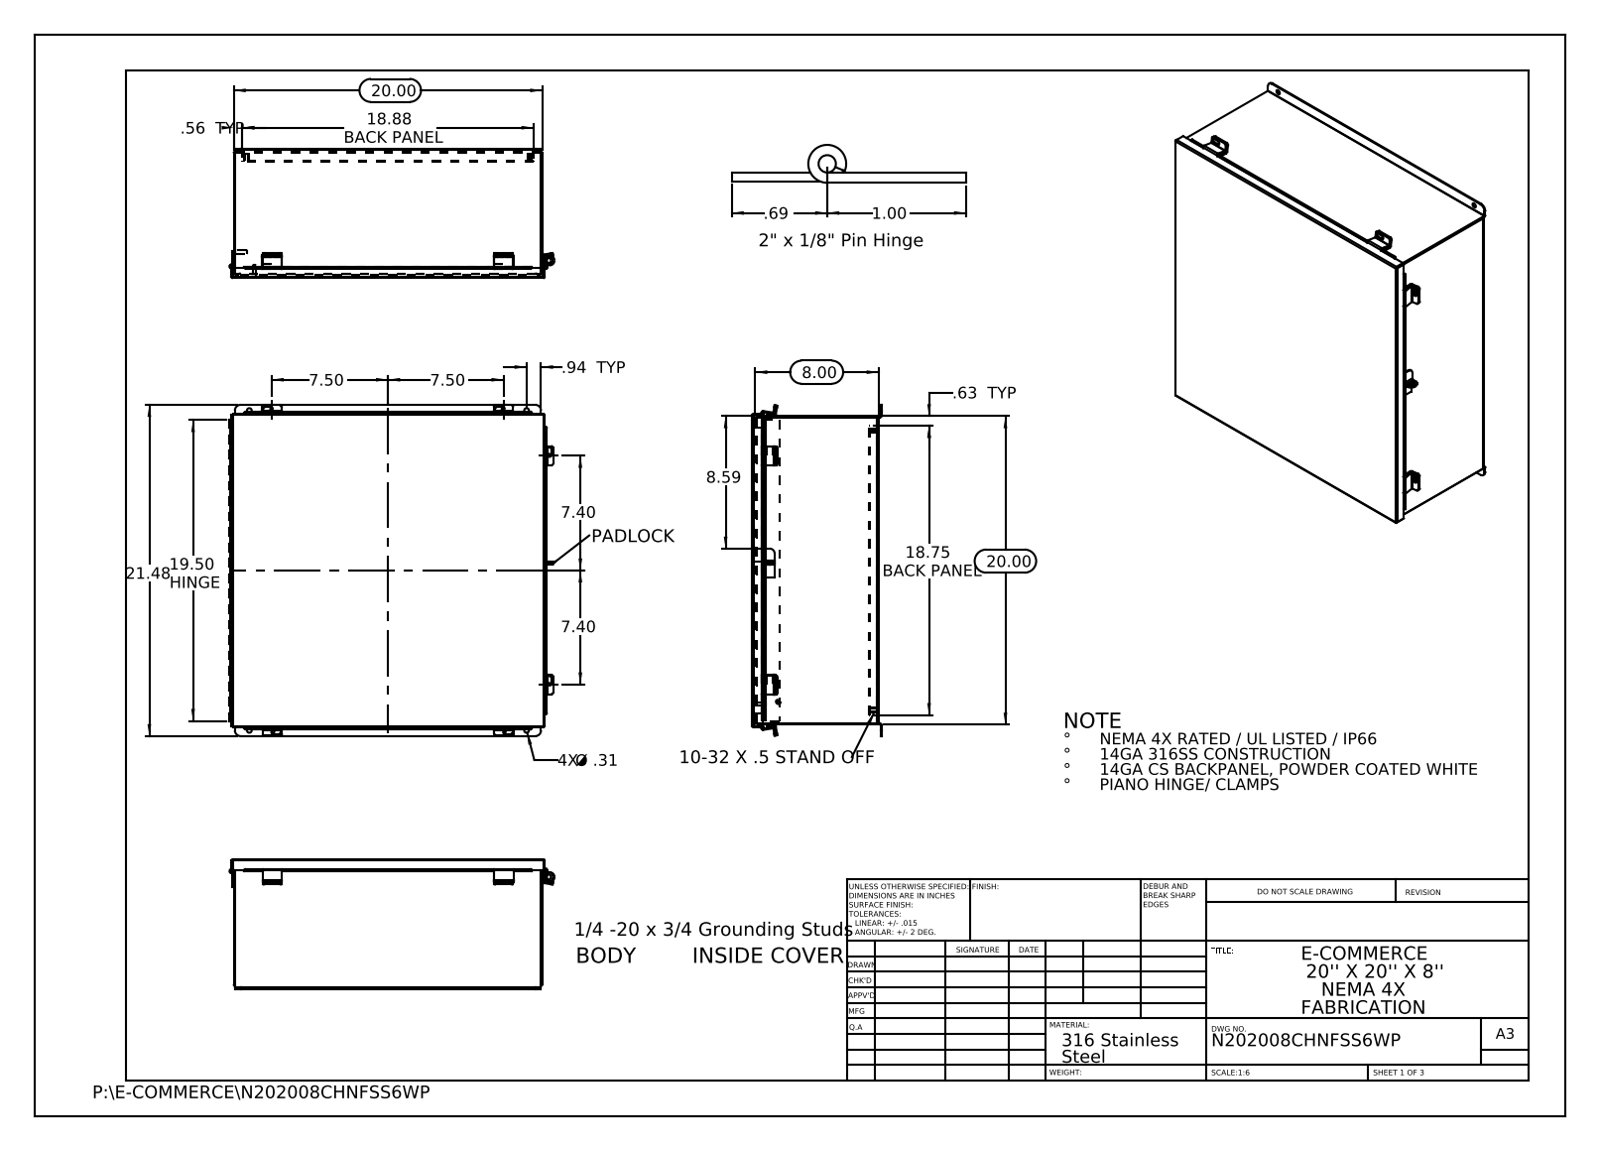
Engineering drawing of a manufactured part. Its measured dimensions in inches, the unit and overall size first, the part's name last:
Units: inches
Overall size (bounding box): 21.476 × 21.072 × 8.39
Round holes (diameter × count): ⌀0.25 ×10, ⌀0.187 ×4, ⌀0.312 ×4, ⌀0.125 ×1, ⌀0.125 ×1, ⌀0.373 ×1, ⌀0.375 ×1
Round bosses / shafts (diameter × count): ⌀0.313 ×4, ⌀0.315 ×2, ⌀0.236 ×2, ⌀0.273 ×1, ⌀0.25 ×1
Partial cylindrical surfaces — rounded edges, fillets, slot ends (radius × count): R0.125 ×24, R0.013 ×13, R0.009 ×12, R0.088 ×12, R0.133 ×12, R0.083 ×6, R0.1 ×6, R0.375 ×4
Main face-to-face distances: 0.075, 8.128, 19.925, 8.053, 8.203, 7.628, 0.575, 0.5, 7.553, 0.649
Hole centre spacings: 1.315, 18.222, 19.427, 26.603, 15, 17.976, 18.126, 18.375
Volume: 147.2 in³ · Surface area: 3 987 in²
Bodies: 27 solids, 938 faces (579 planar, 339 cylindrical, 20 other)
Part name (STEP PRODUCT): N202008CHNFSS6WP HW-CD-S-25020-034; N202008CHNFSS6WP _JIC Hinge; N202008CHNFSS6WP JIC Bottom; HW-CLH-JH-20154 (+8 more)
STEP written by: SolidWorks 2013 (CONFIG_CONTROL_DESIGN)
